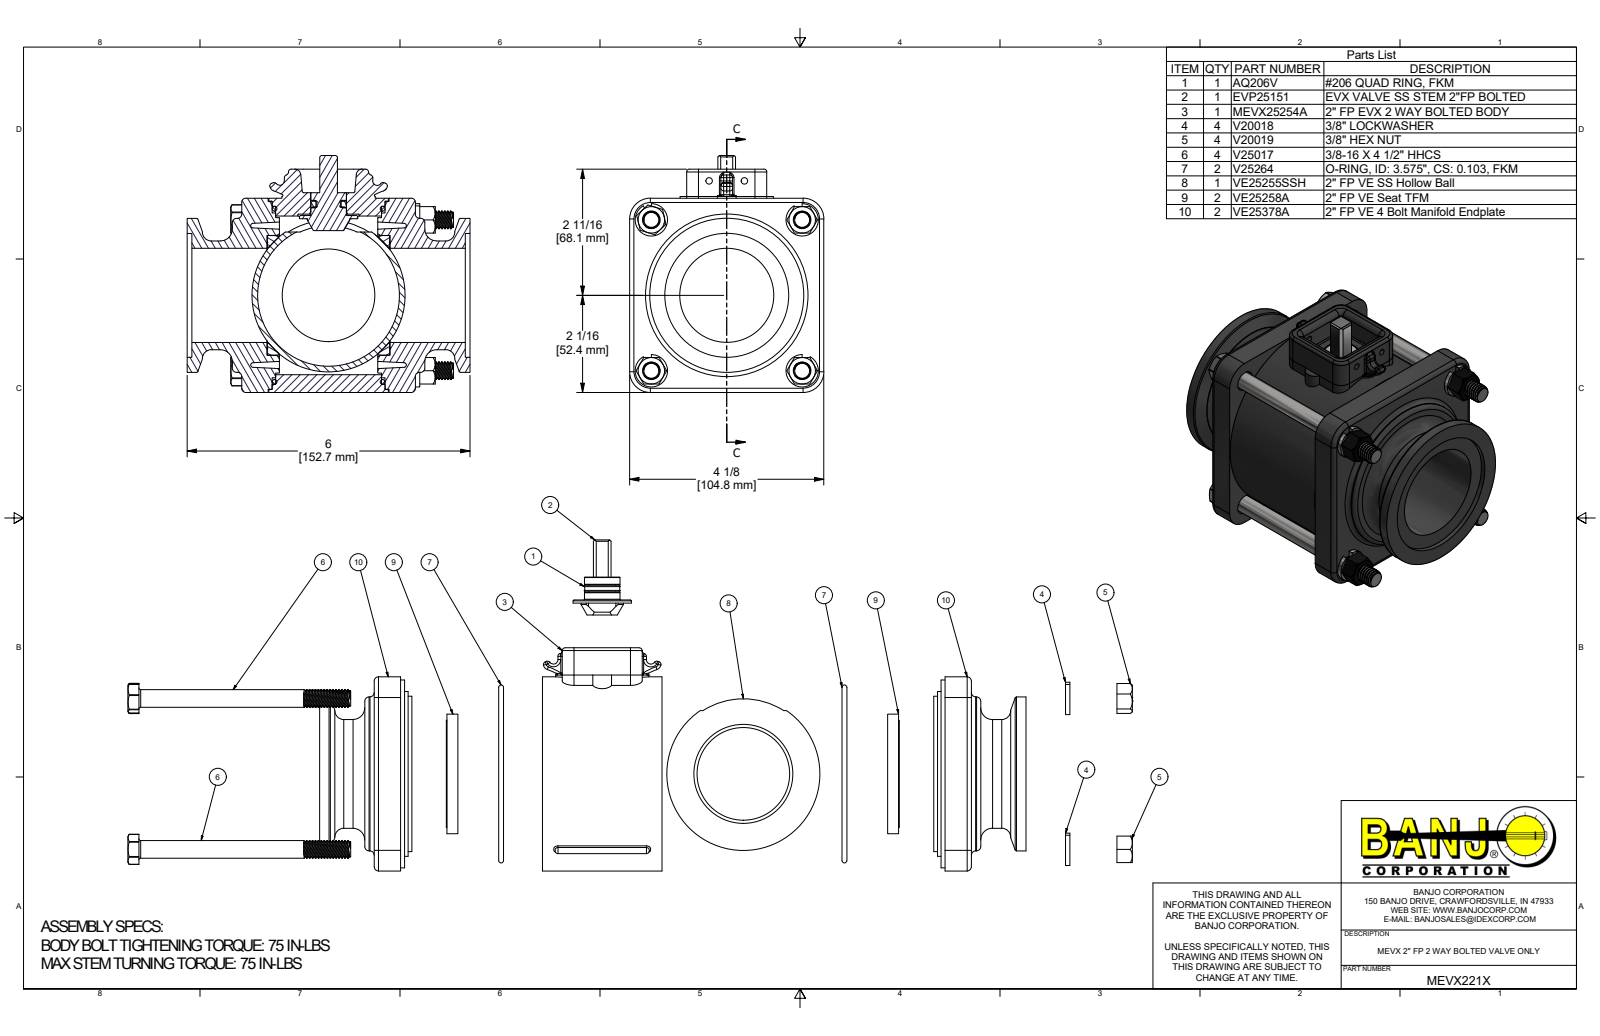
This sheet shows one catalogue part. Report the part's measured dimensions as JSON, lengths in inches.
{"part_name": "MEVX221X; MEVX25254A; MEVX25254AX; V25017 (+8 more)", "step_written_by": "Autodesk Inventor 2019 (AUTOMOTIVE_DESIGN)", "units": "inches", "bodies": {"solids": 22, "faces": 1029, "planar": 218, "cylindrical": 390, "other": 421}, "overall_size": [6.01, 5.031, 4.125], "volume_in3": 40.05, "surface_area_in2": 344.7, "round_holes": [[0.307, 4], [0.385, 4], [0.438, 4], [0.135, 2], [0.76, 1], [1.3, 1], [1.97, 1], [2, 1], [2.045, 1], [2.545, 1], [2.63, 1], [3.37, 1]], "round_bosses_or_shafts": [[0.324, 60], [0.687, 4], [0.375, 4], [4.125, 1], [3.99, 1], [3.5, 1], [3.3, 1], [3.27, 1]], "partial_cylinders_radius": [[0.06, 24], [0.03, 12], [0.09, 10], [0.062, 8], [0.162, 8], [0.125, 6], [0.02, 4], [0.21, 4]], "face_to_face_distances": [0.645, 3.045, 0.56, 3.13, 0.085, 2.485, 0.16, 0.72, 2.97, 2.41], "hole_center_spacings": [2.265, 3.204, 1.48, 2.143, 2.458, 4.214, 4.49, 4.531]}
